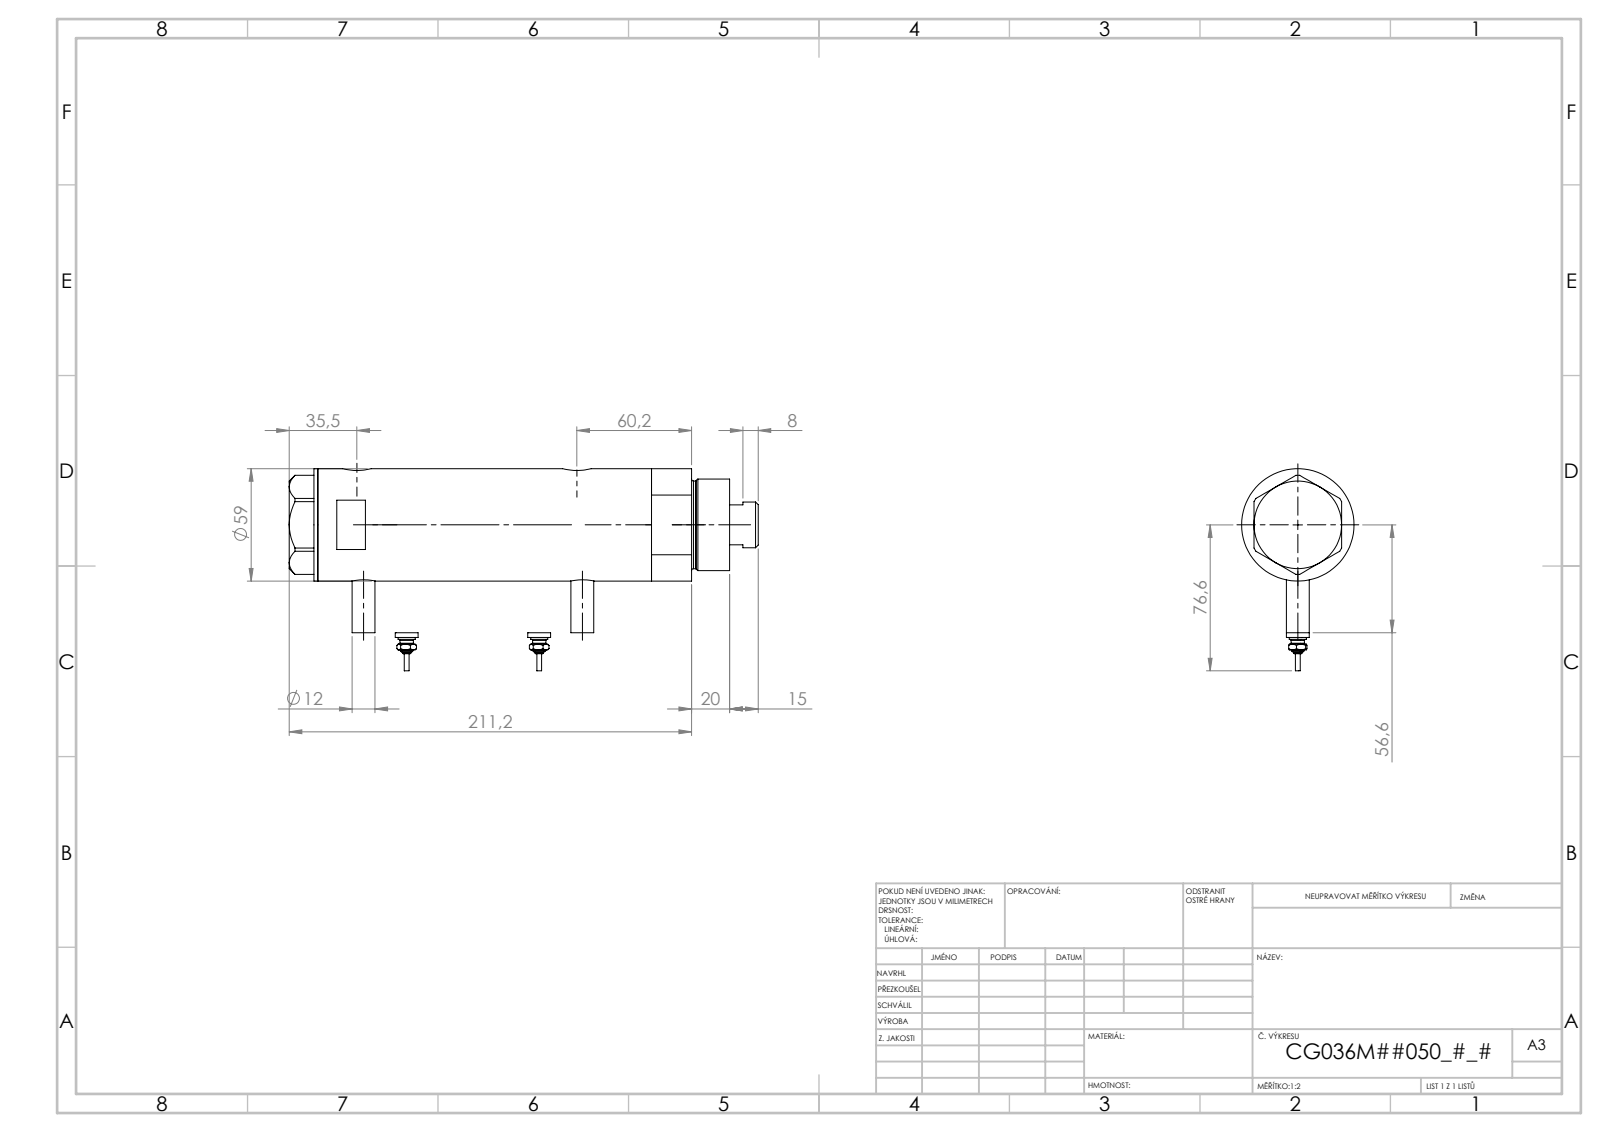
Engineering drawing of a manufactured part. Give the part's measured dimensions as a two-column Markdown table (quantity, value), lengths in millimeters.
| quantity | value |
| --- | --- |
| part name | V270CG_MIDDLE; V270CG_FRONT; V270CG_SWITCH; V270CG_BACK (+1 more) |
| STEP written by | SolidWorks 2019 (CONFIG_CONTROL_DESIGN) |
| units | millimeters |
| bodies | 6 solids, 232 faces (81 planar, 77 cylindrical, 74 other) |
| overall size | 213.42 × 91.3 × 59 |
| volume | 484 346 mm³ |
| surface area | 102 689 mm² |
| round holes (diameter × count) | 5 × 2, 9.73 × 2, 12.5 × 2, 15 × 2, 8.5 × 1, 25 × 1, 26.5 × 1, 36 × 1, 40 × 1, 52 × 1 |
| round bosses / shafts (diameter × count) | 12 × 3, 9 × 2, 7 × 2, 4.34 × 2, 2.4 × 2, 59 × 1, 48 × 1, 46 × 1 |
| main face-to-face distances | 107.35, 38.5, 122.35, 83.85, 15, 15.01, 23.5, 23.49, 107.34, 183.43 |
| hole center spacings | 2.9, 3.5, 82.15, 85.05, 85.65, 88.55, 2.89, 2.91 |
